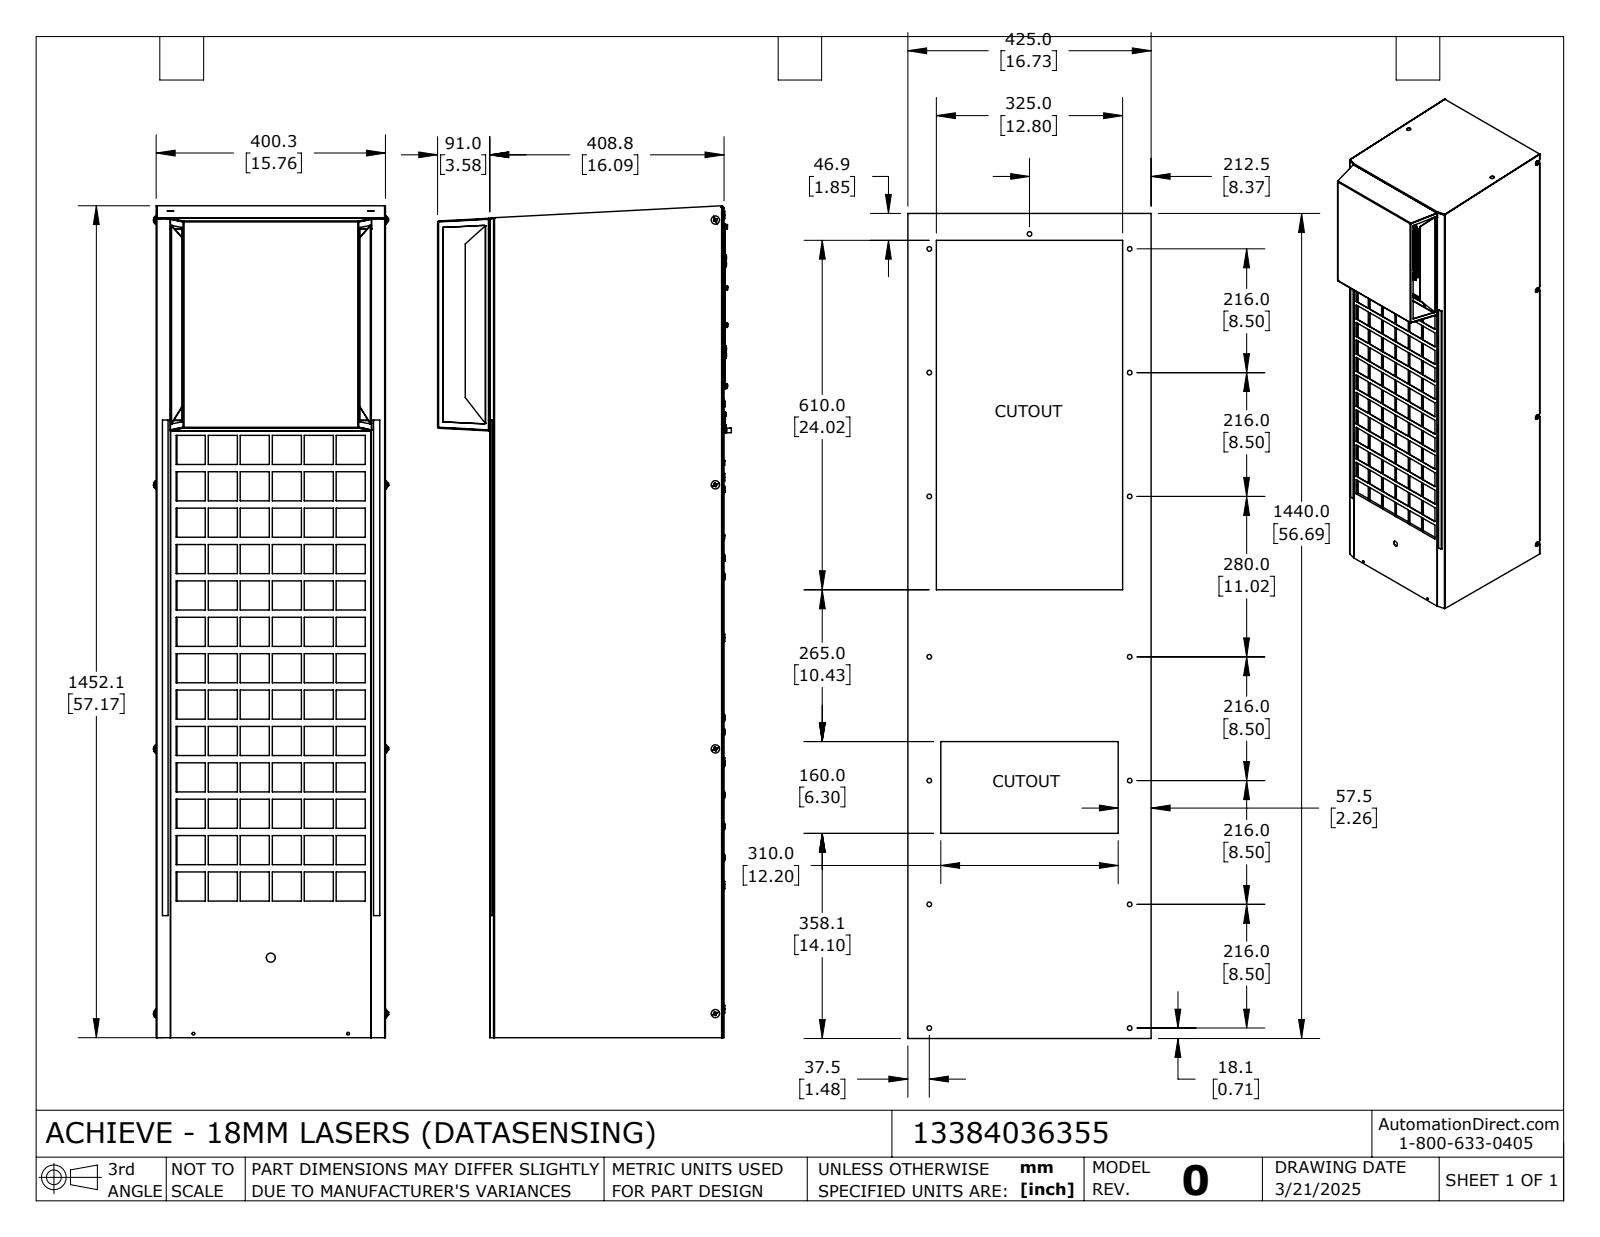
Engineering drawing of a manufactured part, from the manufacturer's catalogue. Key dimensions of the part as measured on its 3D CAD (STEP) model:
Part name (STEP PRODUCT): 13384036355_Default
STEP written by: SolidWorks 2024 (CONFIG_CONTROL_DESIGN)
Units: inches
Bodies: 1 solid, 6463 faces (3532 planar, 1827 cylindrical, 1104 other)
Overall size (bounding box): 57.171 × 20.19 × 16.113
Volume: 13 374 in³ · Surface area: 11 995 in²
Round holes (diameter × count): ⌀0.107 ×48, ⌀0.165 ×47, ⌀0.283 ×18, ⌀0.189 ×14, ⌀0.098 ×4, ⌀0.161 ×4, ⌀0.374 ×4, ⌀0.125 ×2, ⌀0.276 ×2, ⌀0.472 ×2, ⌀0.945 ×2, ⌀0.122 ×1
Round bosses / shafts (diameter × count): ⌀0.178 ×35, ⌀0.512 ×18, ⌀0.315 ×12, ⌀0.157 ×12, ⌀0.122 ×12, ⌀0.354 ×6, ⌀0.079 ×5, ⌀0.573 ×4
Partial cylindrical surfaces — rounded edges, fillets, slot ends (radius × count): R0.125 ×352, R0.031 ×43, R0.076 ×28, R0.198 ×18, R0.087 ×13, R0.132 ×6, R0.083 ×5, R0.118 ×5
Main face-to-face distances: 0.045, 0.045, 0.056, 15.714, 15.759, 15.669, 15.715, 0.28, 0.235, 15.435
Hole centre spacings: 7.48, 14.961, 22.441, 3.028, 0.022, 0.037, 7.874, 29.921
